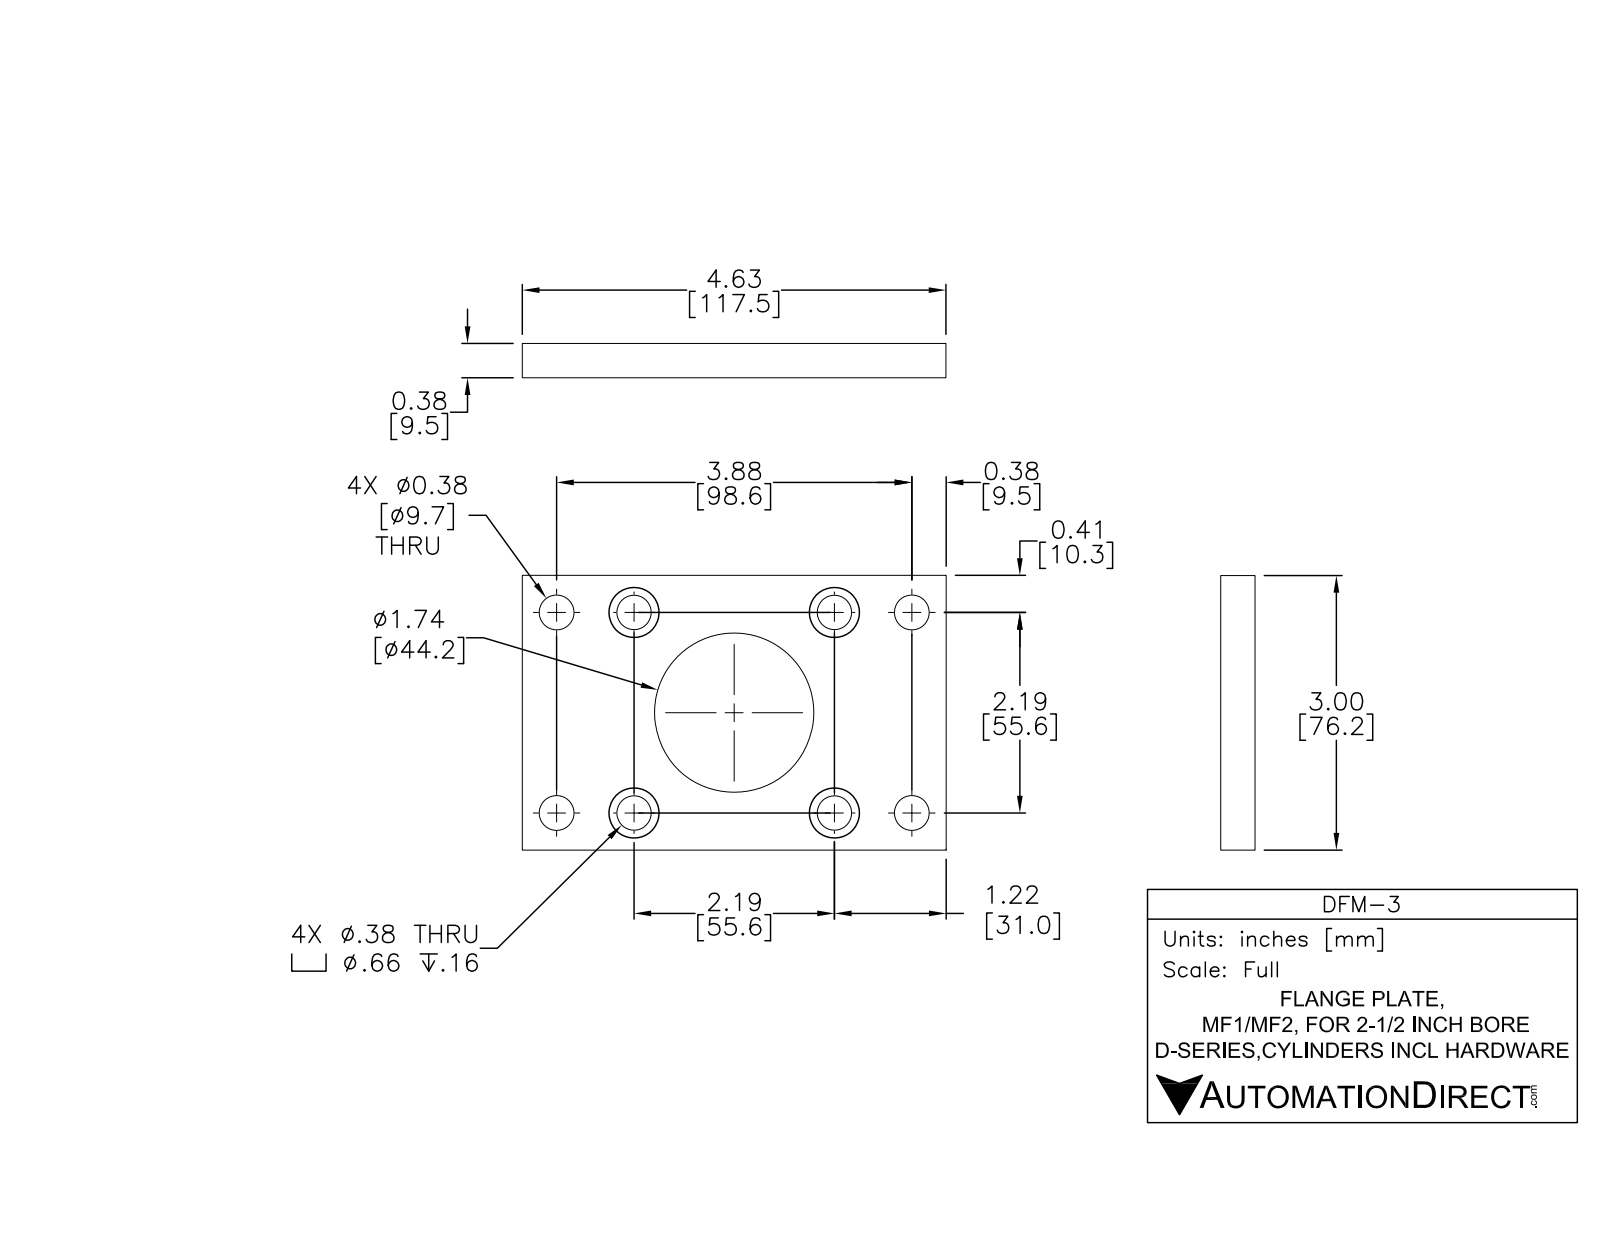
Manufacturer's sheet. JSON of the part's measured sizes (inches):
{"part_name": "DFM-3", "step_written_by": "SolidWorks 2015 (AUTOMOTIVE_DESIGN)", "units": "inches", "bodies": {"solids": 1, "faces": 36, "planar": 10, "cylindrical": 26, "other": 0}, "overall_size": [4.625, 3, 0.375], "volume_in3": 3.845, "surface_area_in2": 33.15, "round_holes": [[0.357, 4], [0.365, 4], [0.675, 2], [0.675, 2], [1.74, 1]], "face_to_face_distances": [0.375, 3, 4.625, 0.155, 0.22], "hole_center_spacings": [2.188, 0.843, 1.547, 2.225, 2.345, 3.031, 3.739, 3.094]}
